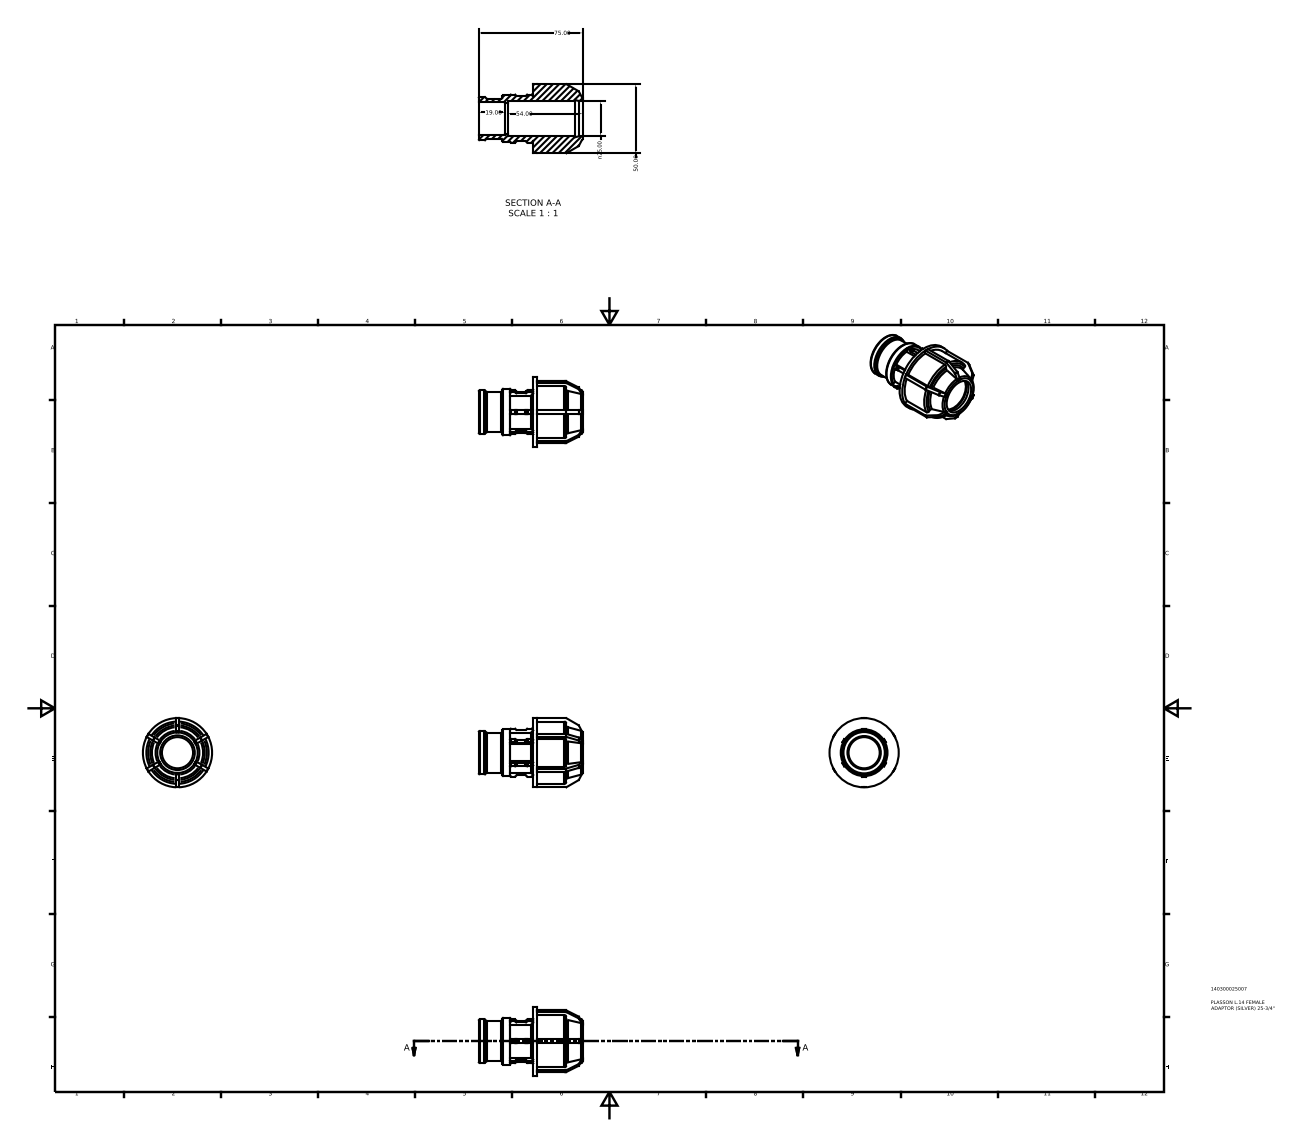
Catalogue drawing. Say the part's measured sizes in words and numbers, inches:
The part is named "140300025007". Its 3-D file was written by "Autodesk Inventor 2015 (AUTOMOTIVE_DESIGN)". It is 1 solid with 262 faces: 160 planar, 68 cylindrical and 34 other. Overall it measures 2.953 by 1.969 by 1.969 inches. Its volume is 2.671 cubic inches and its surface area 29.6 square inches. Round holes: 1 of diameter 0.886, 1 of diameter 0.95, 1 of diameter 0.984. Round bosses or shafts: 1 of diameter 1.969, 1 of diameter 1.772, 1 of diameter 1.329, 1 of diameter 1.234, 1 of diameter 1.139. Partial cylindrical surfaces (rounded edges, fillets, slot ends): 48 of radius 0.03. The main face-to-face distances are 0.098, 0.106, 1.55, 1.656, 1.297, 2.953, 1.403, 2.49, 0.94, 0.834.
